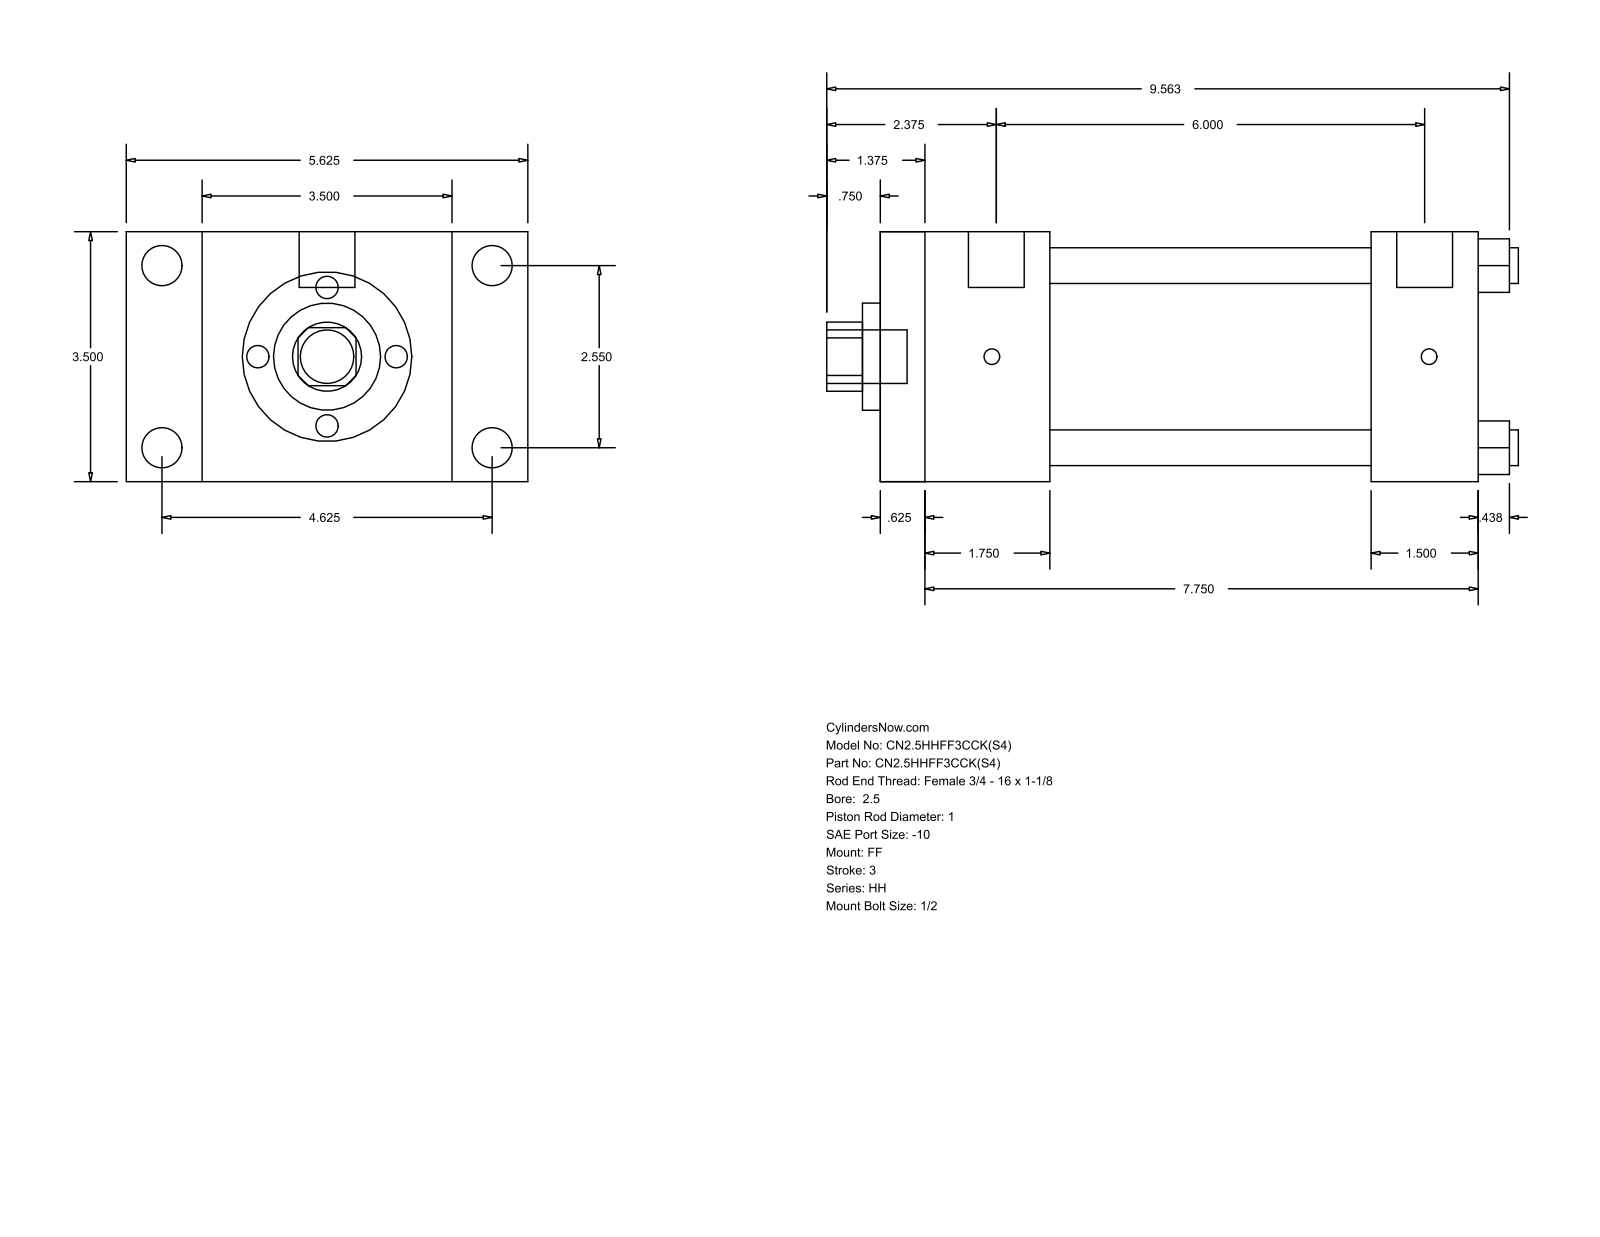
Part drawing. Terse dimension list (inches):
name: HH_FF__0250_1
written by: GSSL Pune (CONFIG_CONTROL_DESIGN)
unit: in
bodies: 0 solids, 92 faces (64 planar, 28 cylindrical, 0 other)
size: 9.687 × 5.625 × 3.5
holes: 4× ⌀0.5, 1× ⌀1, 1× ⌀1.5, 1× ⌀2.875
bosses: 4× ⌀0.563, 4× ⌀0.219, 2× ⌀0.781, 1× ⌀0.75
rounds: 1× R0.484
face distances: 3.5, 8.375, 0.625, 7.75, 2.375, 1.75, 6, 6.875, 6.25, 4.5
hole spacings: 1.803, 2.55, 3.606
